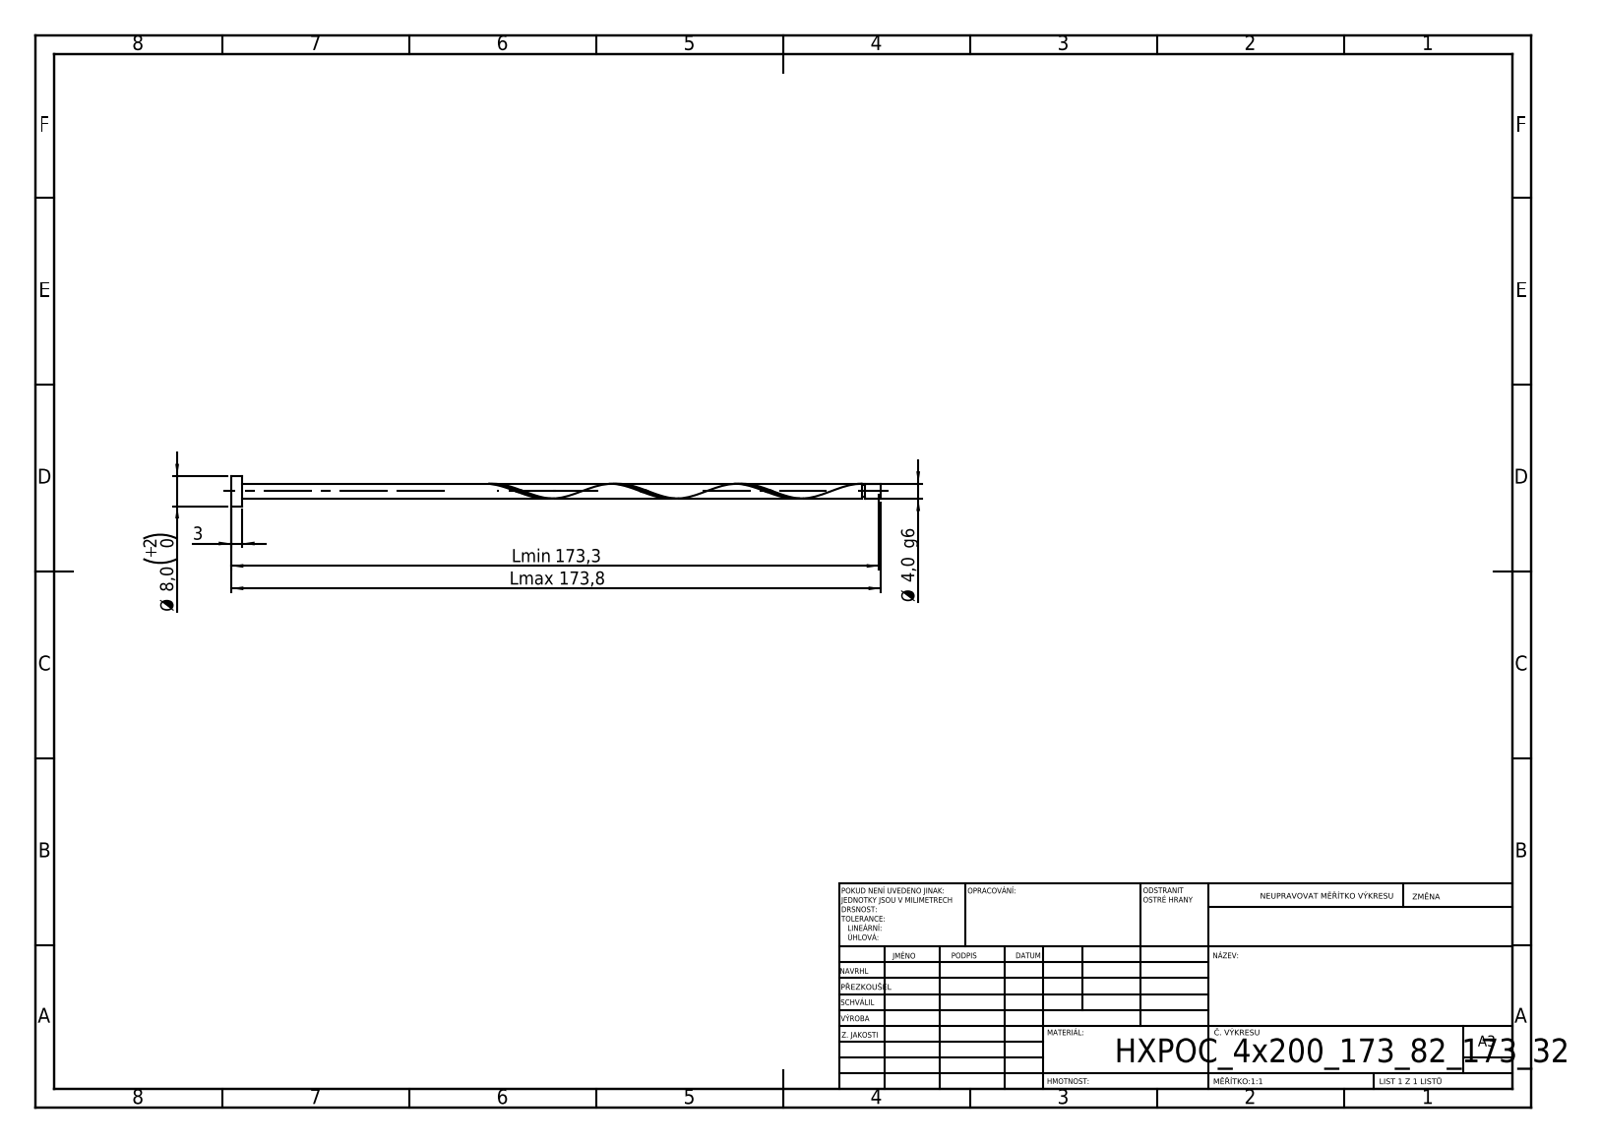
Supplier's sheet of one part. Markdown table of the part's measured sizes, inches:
| quantity | value |
| --- | --- |
| part name | a515 |
| STEP written by | SolidWorks 2019 (CONFIG_CONTROL_DESIGN) |
| units | inches |
| bodies | 1 solid, 21 faces (6 planar, 14 cylindrical, 1 other) |
| overall size | 6.843 × 0.315 × 0.315 |
| volume | 0.139 in³ |
| surface area | 3.675 in² |
| round bosses / shafts (diameter × count) | 0.315 × 1, 0.157 × 1, 0.126 × 1 |
| main face-to-face distances | 0.118, 6.843, 6.725, 6.679, 6.561, 0.164, 6.648, 6.53, 0.031, 0.196 |
